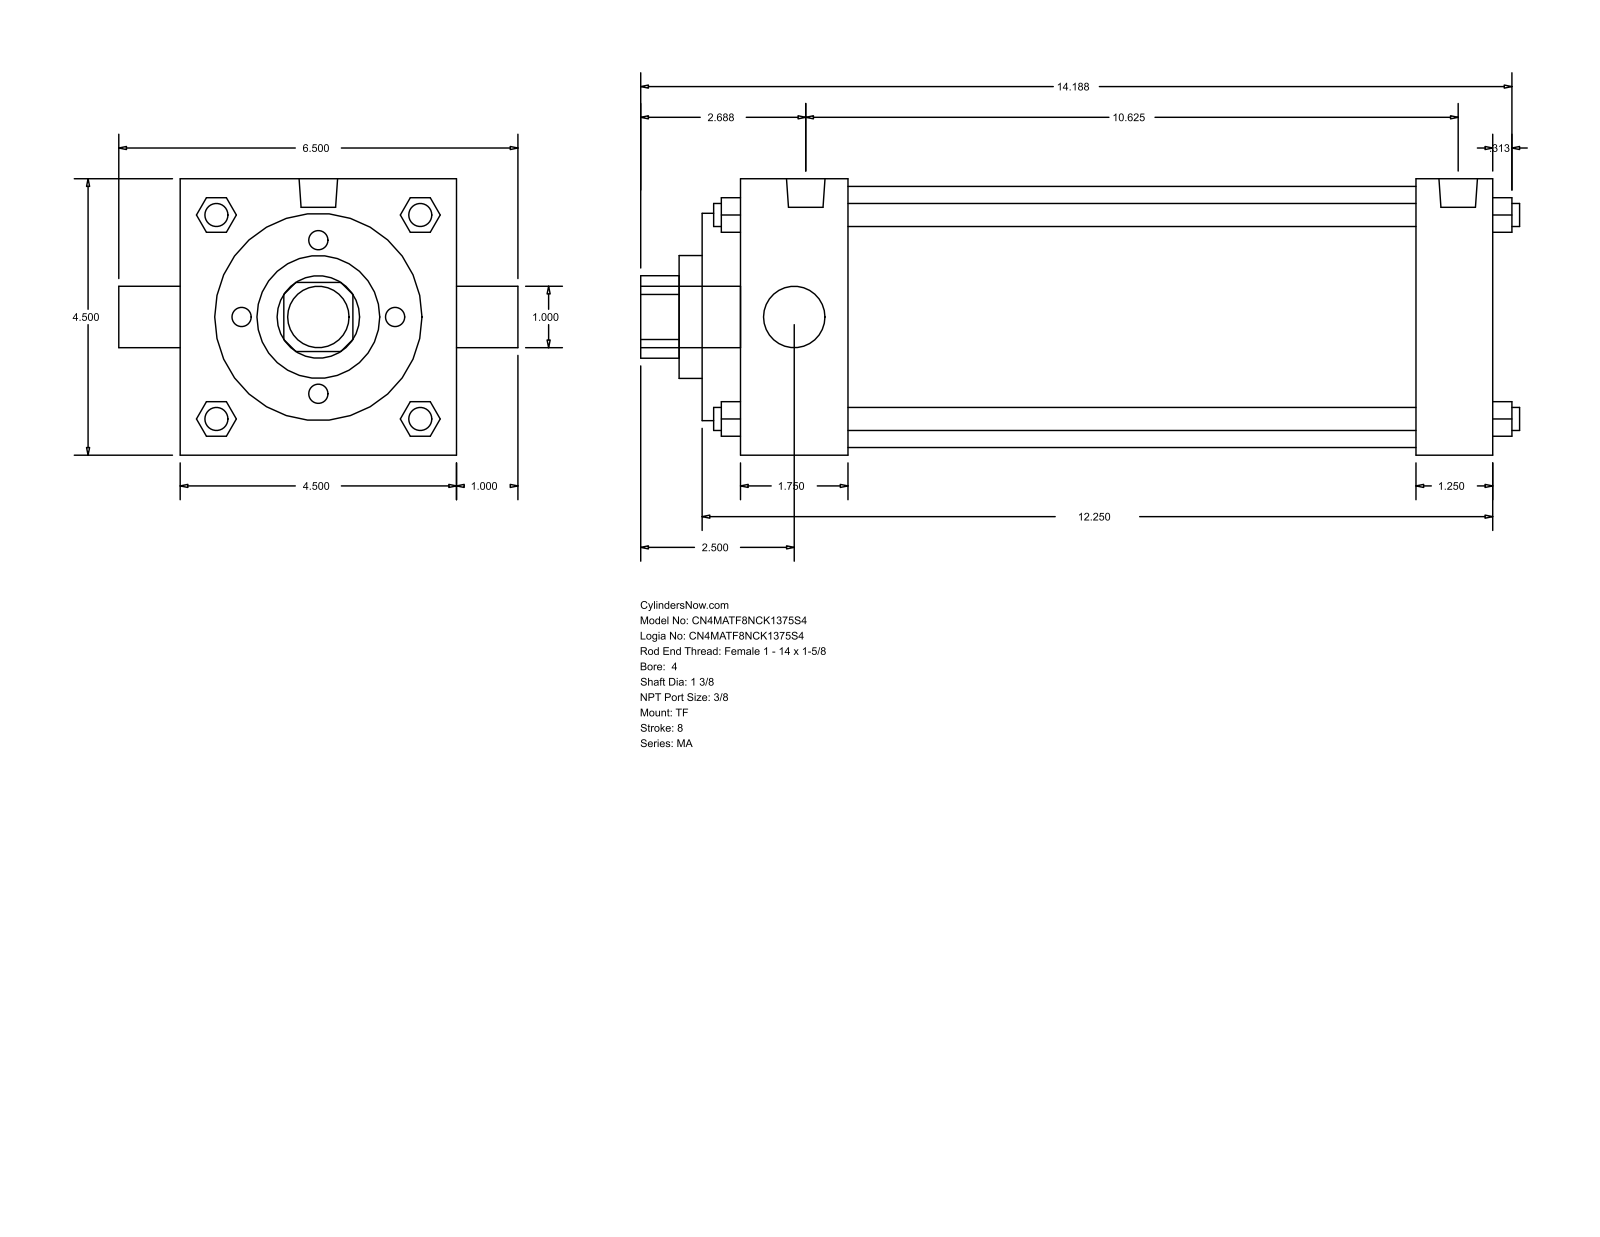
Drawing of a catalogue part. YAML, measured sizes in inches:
part_name: "MA_TF__0400_1.375"
step_written_by: "GSSL Pune (CONFIG_CONTROL_DESIGN)"
units: inches
bodies: {solids: 0, faces: 122, planar: 93, cylindrical: 29, other: 0}
overall_size: [14.313, 6.5, 4.5]
round_holes:
  - {diameter: 1, count: 1}
  - {diameter: 1.375, count: 1}
  - {diameter: 2, count: 1}
  - {diameter: 3.375, count: 1}
  - {diameter: 4.25, count: 1}
round_bosses_or_shafts:
  - {diameter: 0.375, count: 4}
  - {diameter: 0.437, count: 3}
  - {diameter: 0.627, count: 2}
  - {diameter: 1, count: 1}
partial_cylinders:
  - {radius: 0.672, count: 1}
face_to_face_distances: [4.5, 12.25, 0.625, 12.875, 11.625, 11, 1.25, 2.375, 1.75, 9.25]
